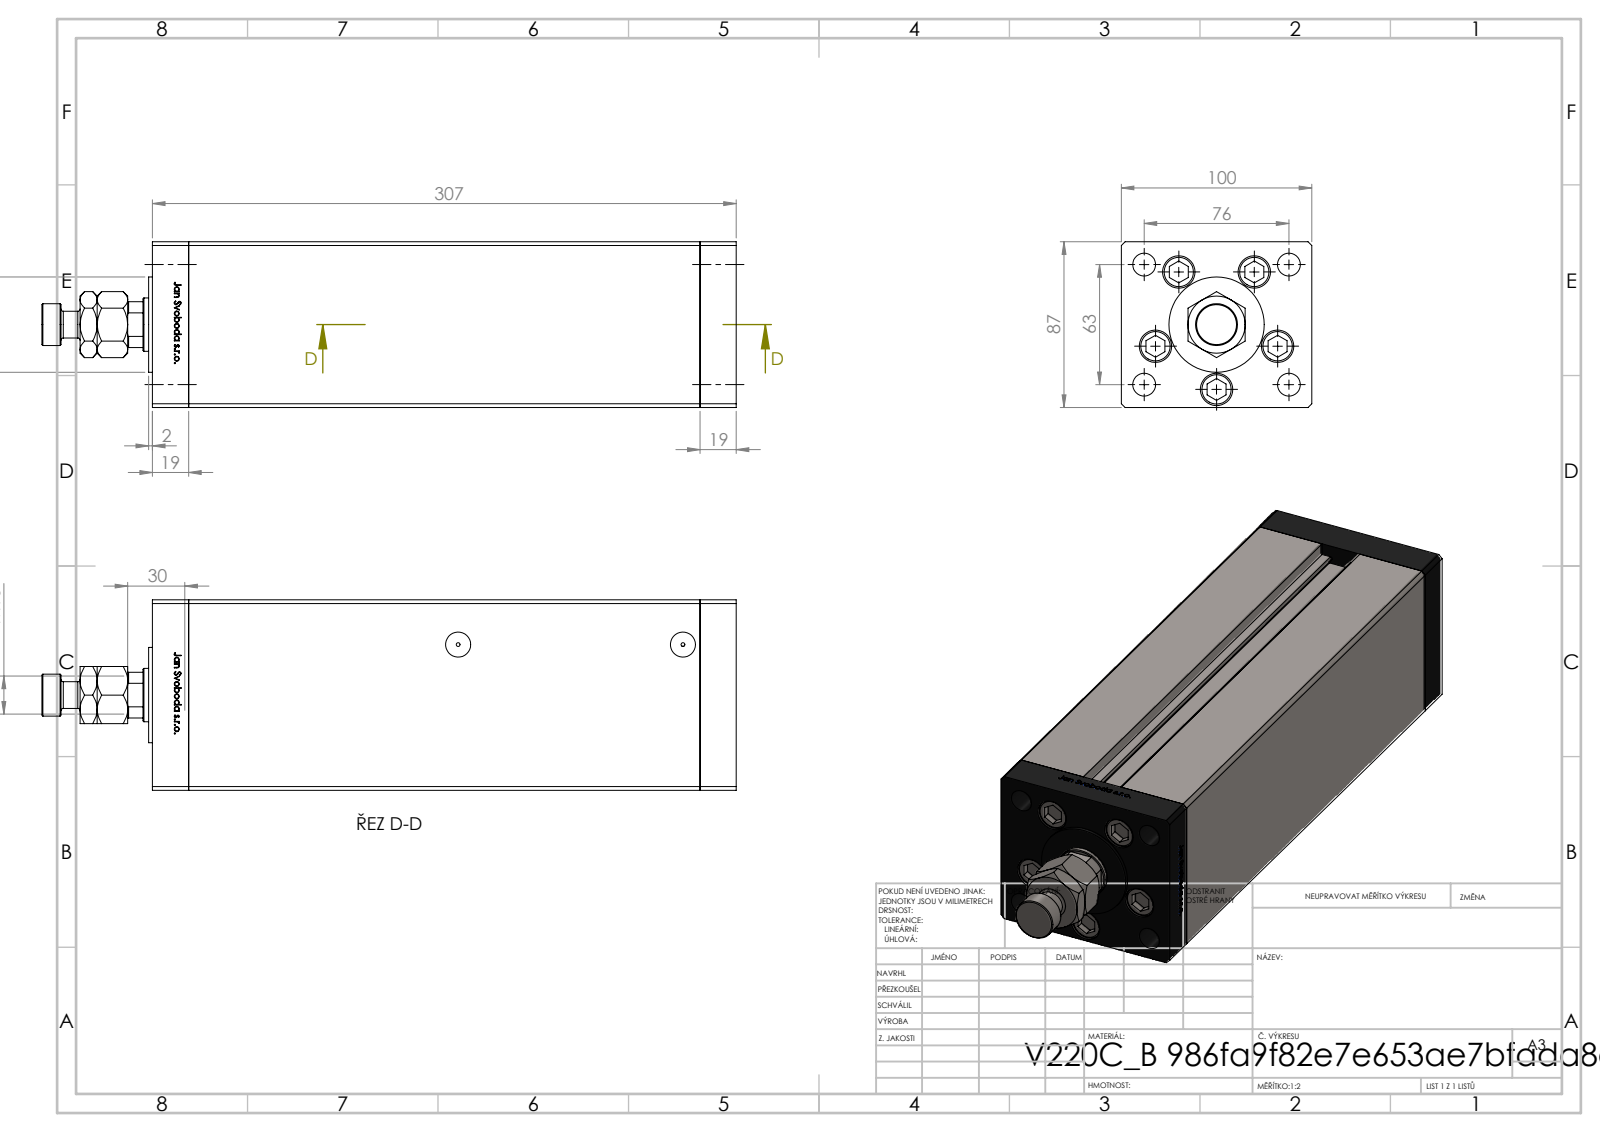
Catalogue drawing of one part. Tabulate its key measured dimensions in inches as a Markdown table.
| quantity | value |
| --- | --- |
| part name | V220C_FRONT_B; V220C_B MIDDLE; MFA; V220C BACK_B (+2 more) |
| STEP written by | SolidWorks 2019 (CONFIG_CONTROL_DESIGN) |
| units | inches |
| bodies | 15 solids, 1237 faces (480 planar, 151 cylindrical, 606 other) |
| overall size | 14.35 × 3.937 × 3.425 |
| volume | 141.3 in³ |
| surface area | 445.7 in² |
| round holes (diameter × count) | 0.531 × 7, 0.669 × 5, 0.472 × 4, 0.079 × 2, 0.518 × 2, 0.728 × 1, 1.102 × 1 |
| round bosses / shafts (diameter × count) | 0.315 × 5, 0.669 × 2, 1.969 × 1, 0.866 × 1, 0.551 × 1 |
| partial cylindrical surfaces (radius × count) | 0.037 × 2, 0.531 × 1 |
| main face-to-face distances | 3.937, 3.425, 0.748, 10.571, 11.319, 1.348, 12.067, 0.6, 9.97, 10.719 |
| hole center spacings | 1.339, 0.732, 1.561, 1.943, 2.281, 0.828, 1.499, 1.546 |
